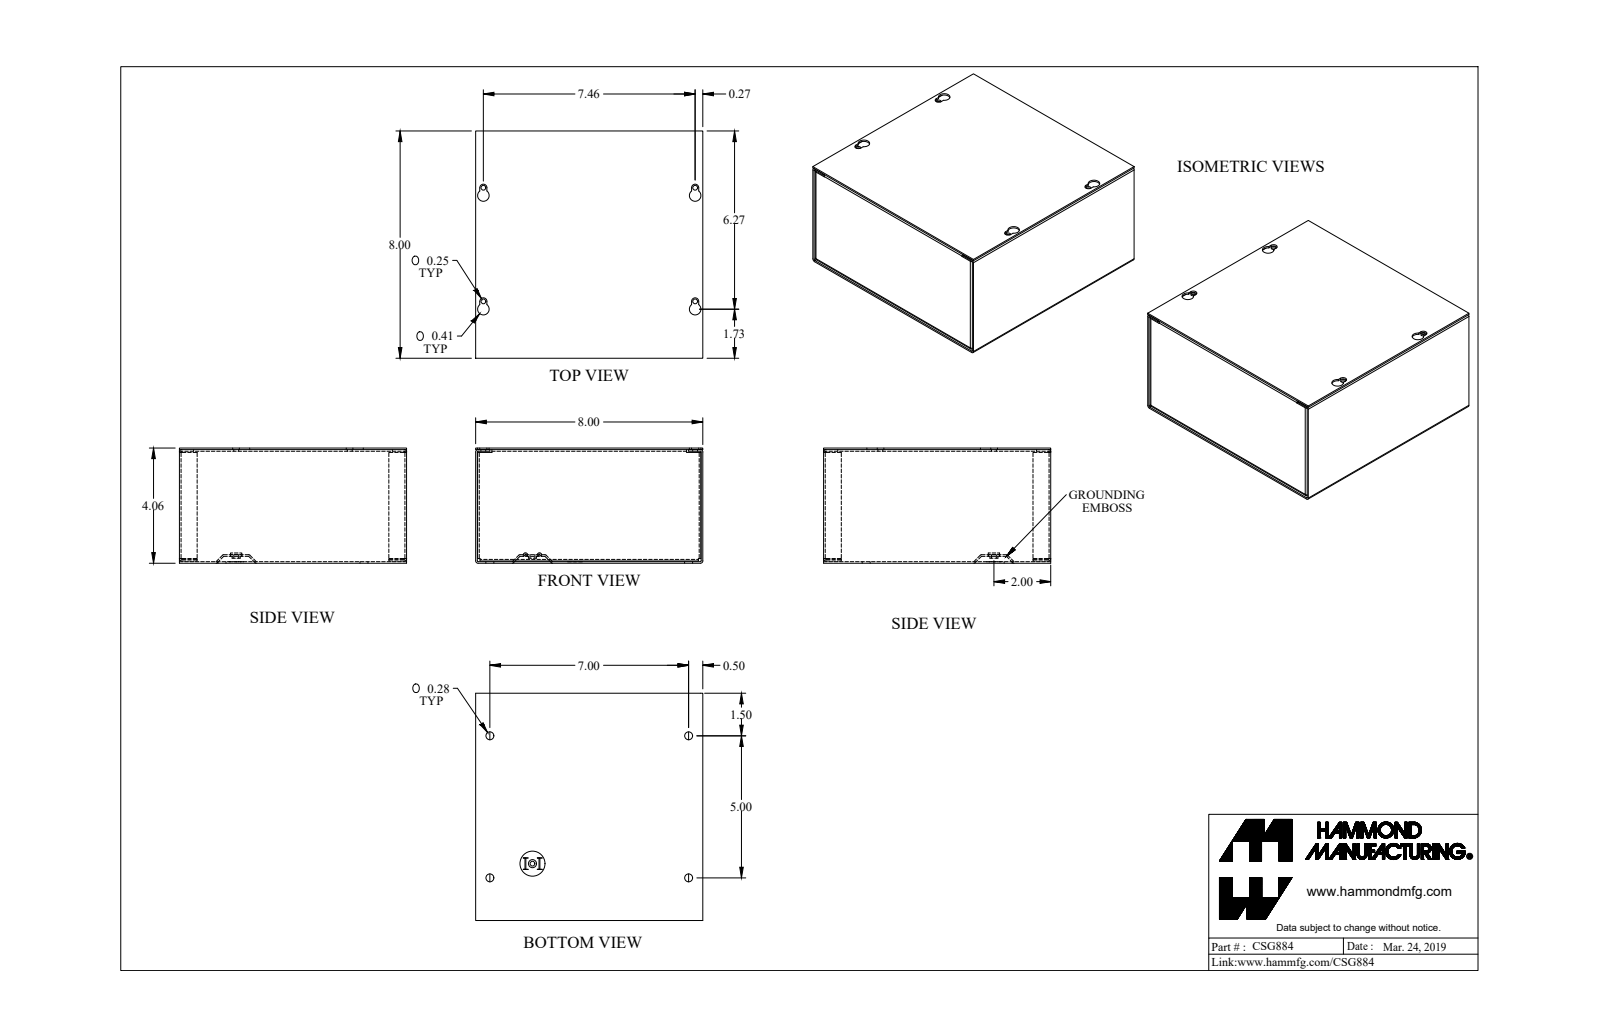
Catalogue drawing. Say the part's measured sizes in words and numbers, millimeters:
The part is named "CSG884_Default". Its 3-D file was written by "SolidWorks 2019 (CONFIG_CONTROL_DESIGN)". It is 4 solids with 205 faces: 125 planar, 72 cylindrical and 8 other. Overall it measures 203.2 by 203.2 by 103 millimeters. Its volume is 261 900 cubic millimeters and its surface area 367 400 square millimeters. Round holes: 5 of diameter 4.3, 4 of diameter 7.1, 1 of diameter 12.7. Round bosses or shafts: 1 of diameter 12.5, 1 of diameter 7.2. Partial cylindrical surfaces (rounded edges, fillets, slot ends): 12 of radius 0.7, 12 of radius 2.2, 8 of radius 1.4, 4 of radius 3.2, 4 of radius 5.2. The main face-to-face distances are 1.4, 101.6, 201.8, 100.2, 203.2, 103, 200.3, 2, 98.1, 99.6. The hole center spacings are 14, 114.5, 184.1, 216.3, 101.6, 127, 177.8, 189.5.
